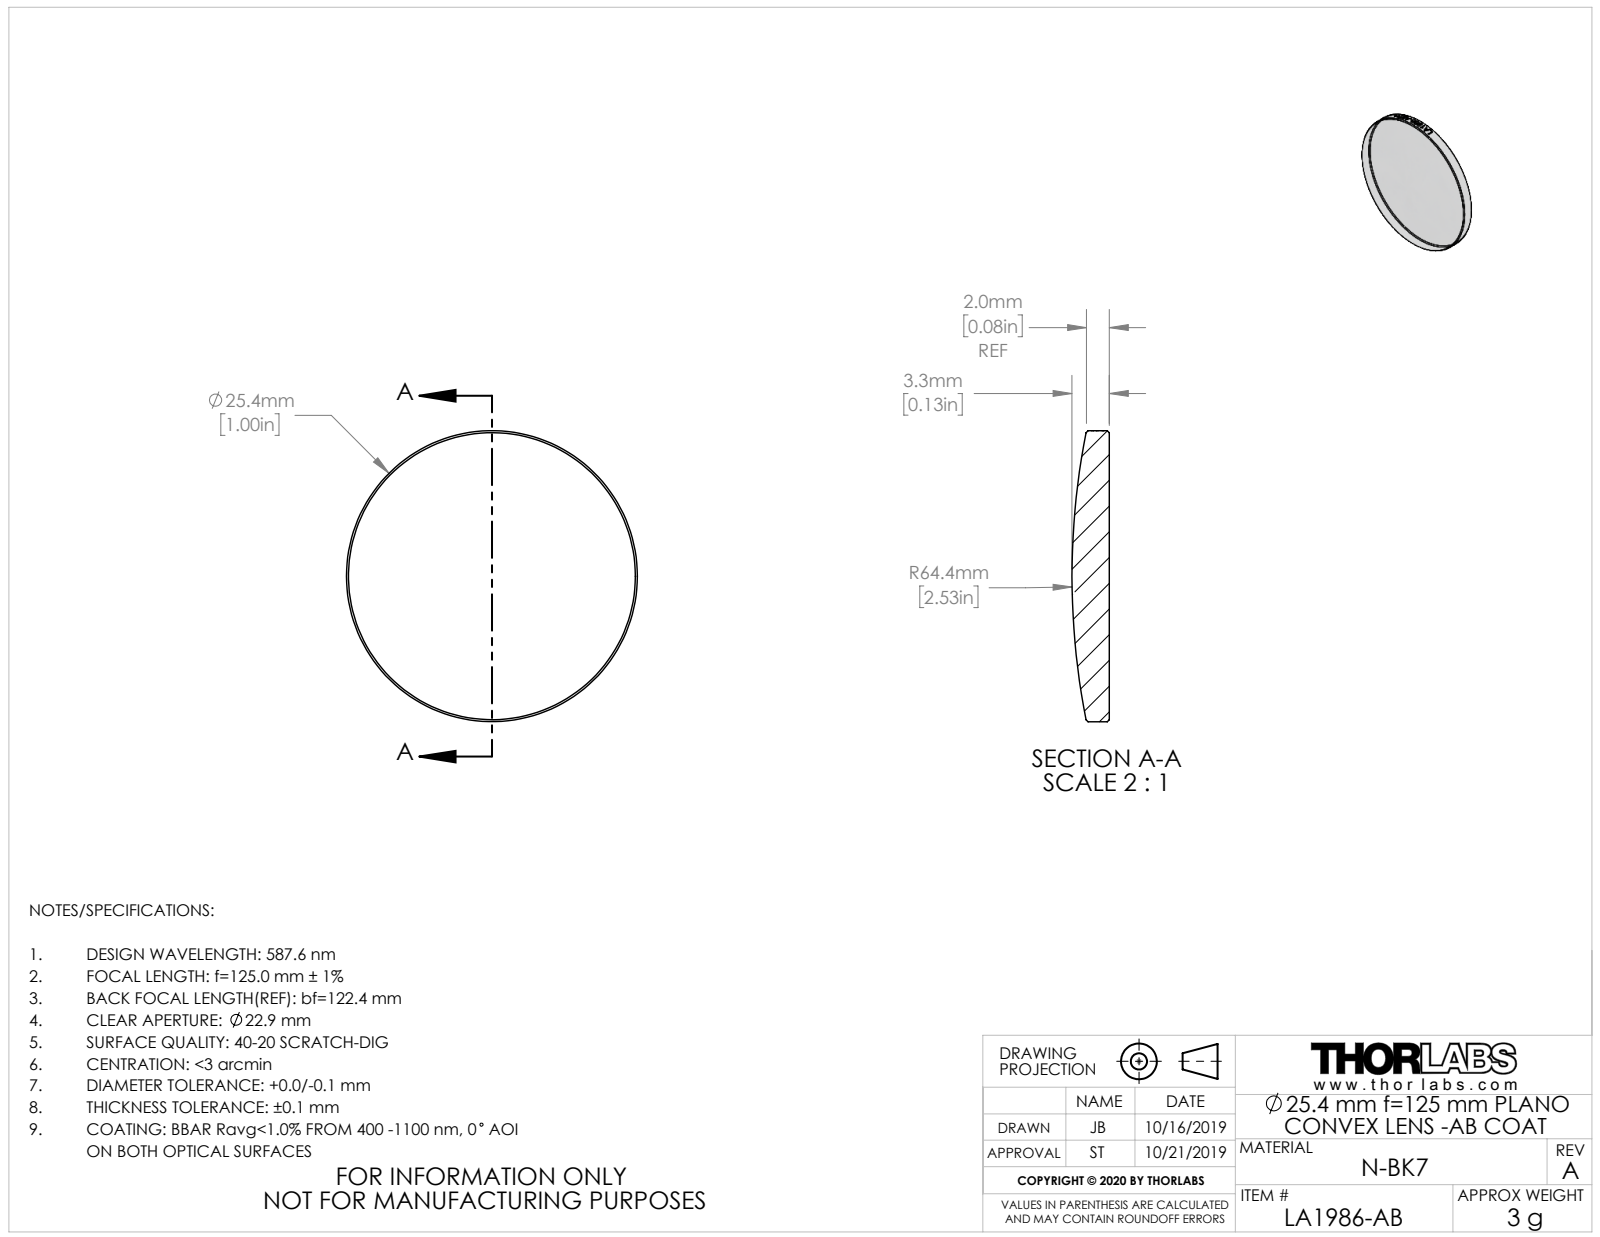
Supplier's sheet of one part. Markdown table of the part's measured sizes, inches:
| quantity | value |
| --- | --- |
| part name | TTN195771-E0W |
| STEP written by | SolidWorks 2018 (CONFIG_CONTROL_DESIGN) |
| units | inches |
| bodies | 1 solid, 30 faces (1 planar, 23 cylindrical, 6 other) |
| overall size | 1 × 1 × 0.128 |
| volume | 0.081 in³ |
| surface area | 1.804 in² |
| round bosses / shafts (diameter × count) | 1 × 1 |
